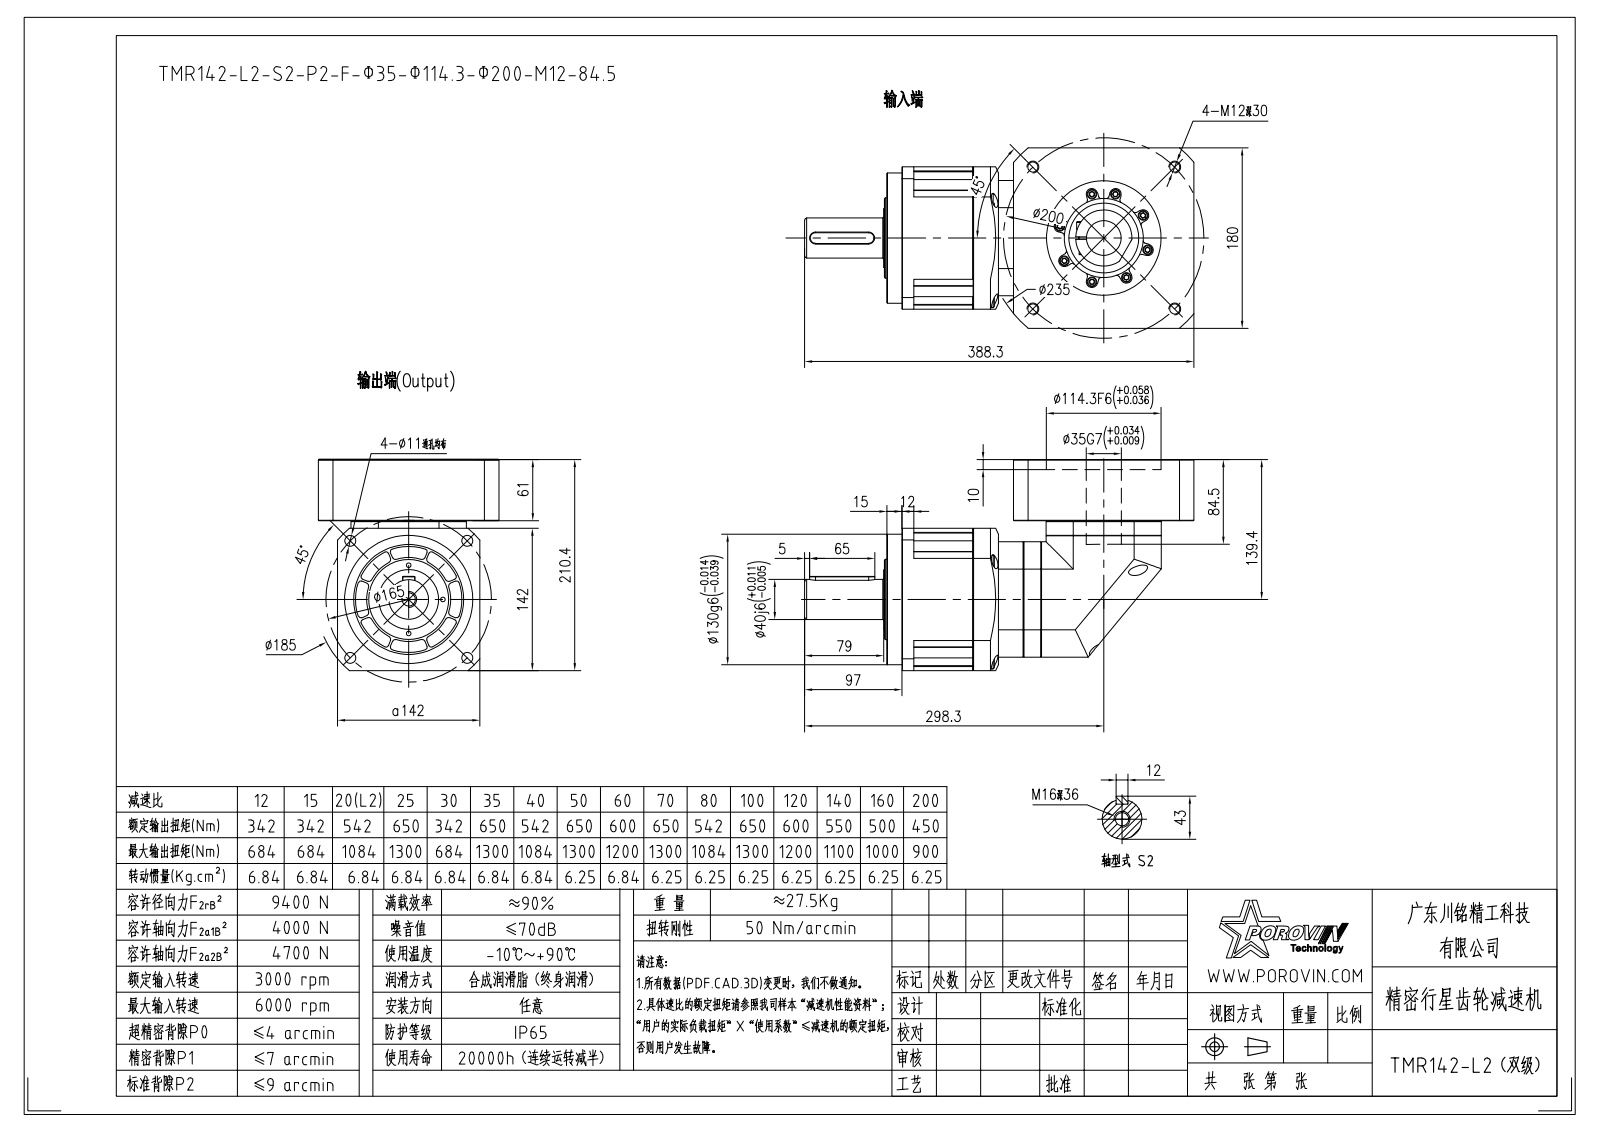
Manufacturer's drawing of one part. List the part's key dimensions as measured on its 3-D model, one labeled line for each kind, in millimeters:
Part name (STEP PRODUCT): SPRING_LOCK_WASHERS--NORMAL_TYP; HEXAGON_SOCKET_HEAD_CAP_SC-7702; HEXAGON_SOCKET_HEAD_CAP_S-29686; HEXAGON_SOCKET_HEAD_CAP_SC-7651 (+8 more)
STEP written by: CREO PARAMETRIC BY PTC INC, 2020053 (CONFIG_CONTROL_DESIGN)
Units: millimetres
Bodies: 49 solids, 1556 faces (653 planar, 607 cylindrical, 296 other)
Overall size (bounding box): 389.52 × 210.4 × 182.45
Volume: 5 227 000 mm³ · Surface area: 498 308 mm²
Round holes (diameter × count): ⌀6.5 ×18, ⌀6.68 ×17, ⌀5 ×13, ⌀11 ×10, ⌀6.8 ×7, ⌀14 ×5, ⌀9 ×4, ⌀10.2 ×4, ⌀10.5 ×4, ⌀8.5 ×1, ⌀13.6 ×1, ⌀17 ×1
Round bosses / shafts (diameter × count): ⌀10 ×17, ⌀9.88 ×17, ⌀6 ×17, ⌀13 ×5, ⌀8 ×5, ⌀130 ×1, ⌀99 ×1, ⌀80 ×1
Partial cylindrical surfaces — rounded edges, fillets, slot ends (radius × count): R2 ×48, R1 ×40, R5.75 ×8, R10.5 ×4, R6 ×2, R65 ×2, R5 ×1, R6.75 ×1
Main face-to-face distances: 13.5, 128.5, 50.3, 61, 18, 180.02, 68.3, 68.1, 17.8, 142
Hole centre spacings: 45.25, 83.61, 34.63, 63.99, 90.5, 0.74, 12.31, 21.17
